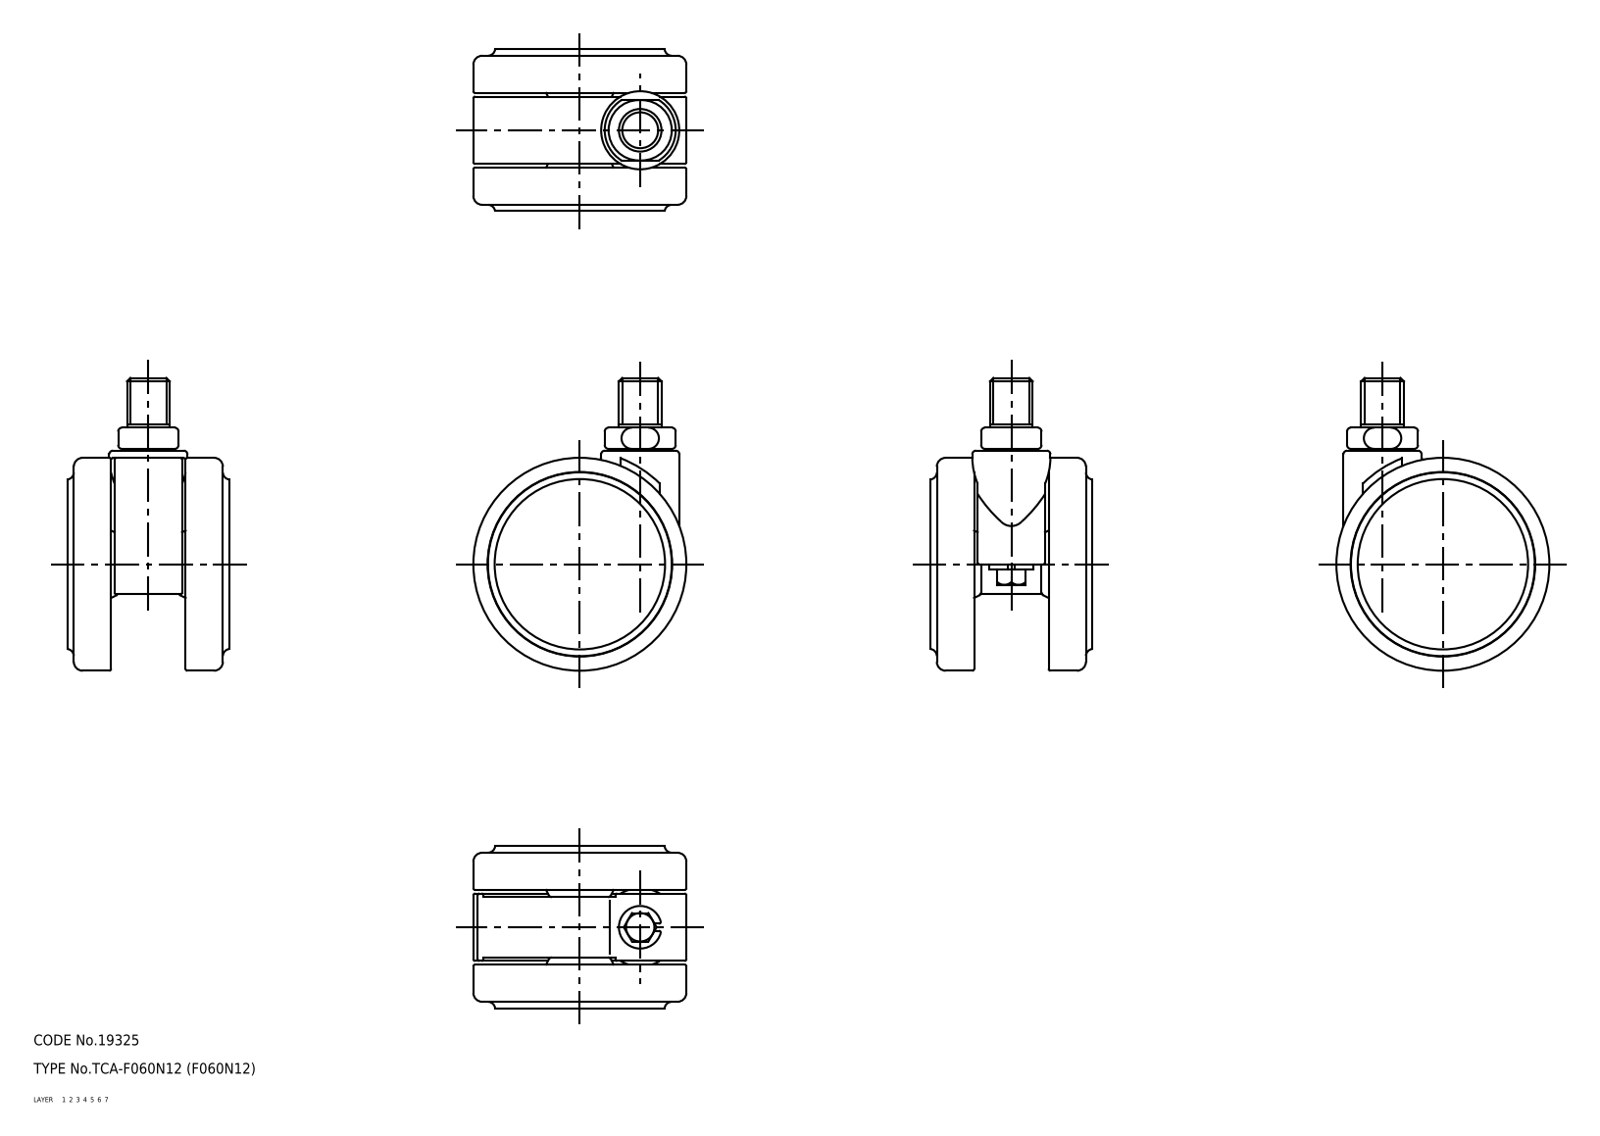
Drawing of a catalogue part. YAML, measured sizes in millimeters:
part_name: "67118946; 67118959; 67118972; 67118985"
step_written_by: "CADfix (AUTOMOTIVE_DESIGN)"
units: millimeters
bodies: {solids: 4, faces: 150, planar: 0, cylindrical: 0, other: 150}
overall_size: [82.5, 60, 45.6]
volume: 86784
surface_area: 27529
